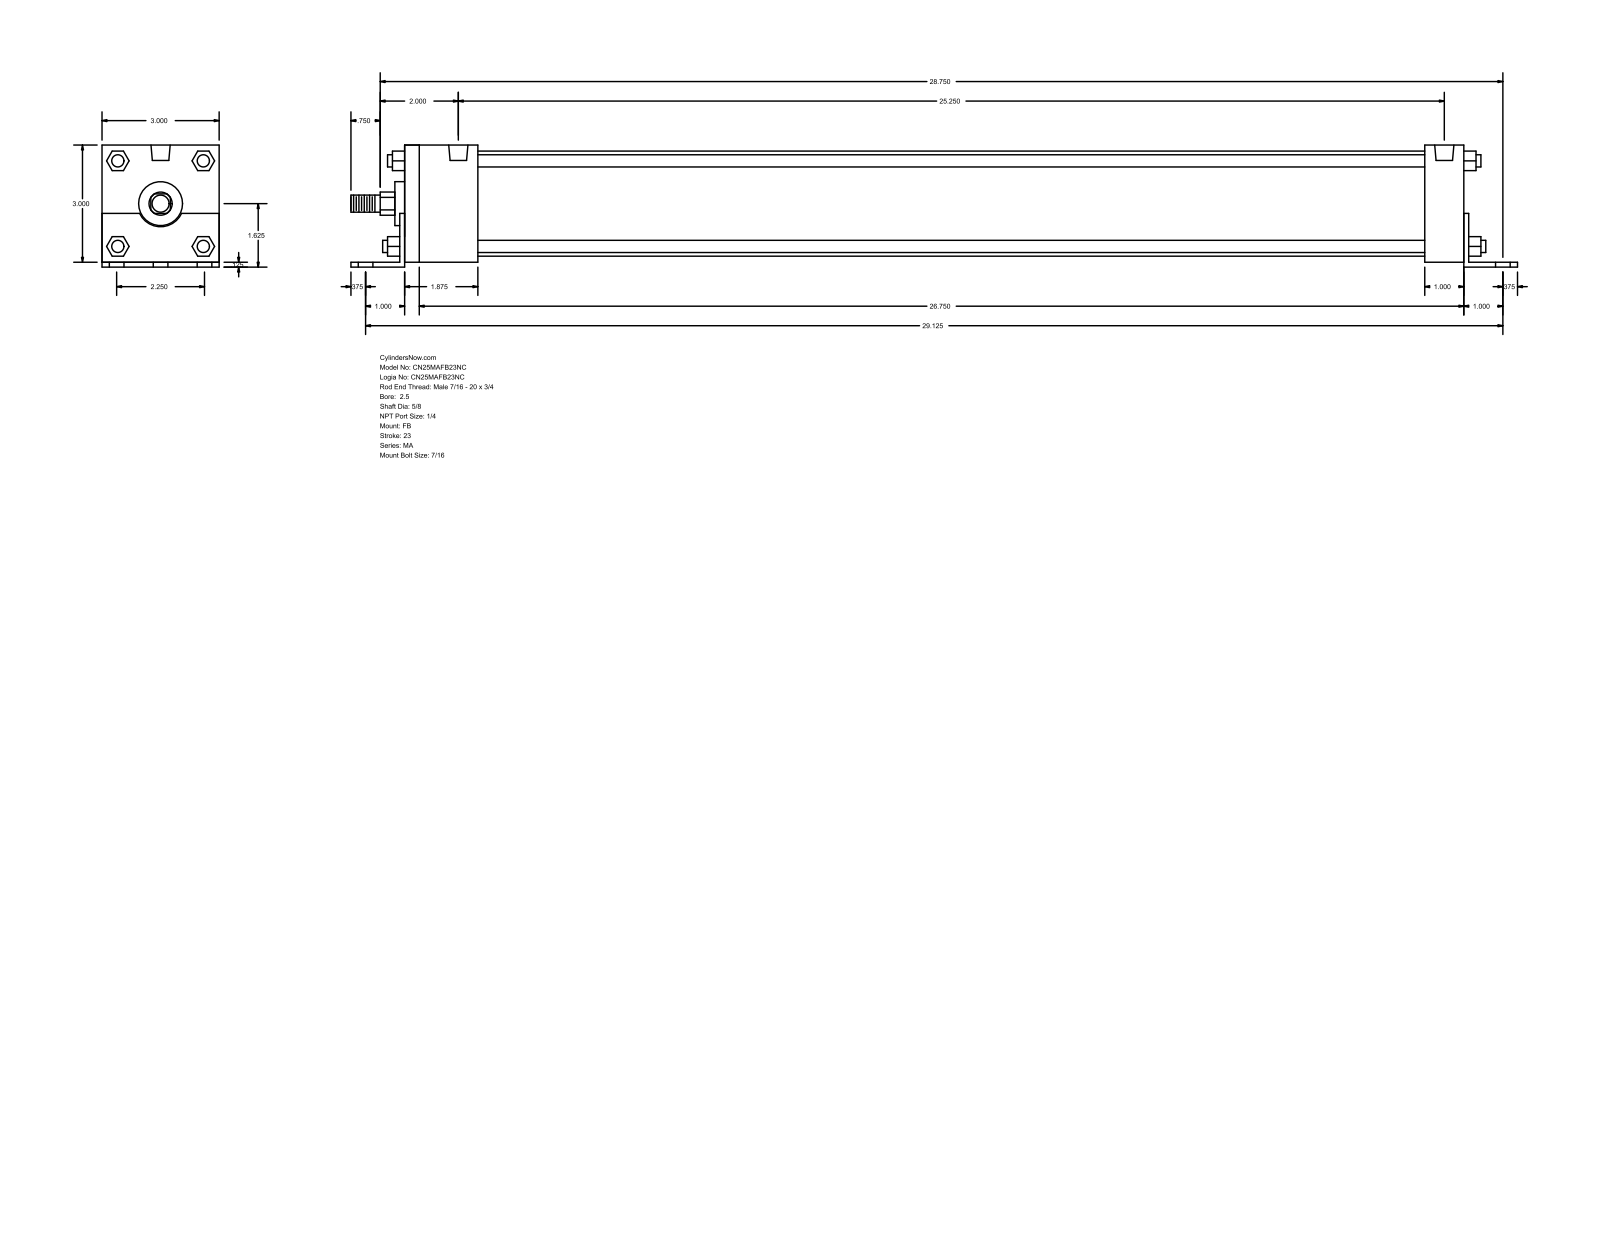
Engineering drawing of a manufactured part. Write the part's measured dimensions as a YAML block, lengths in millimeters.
part_name: "MA_FB__0250_0.625"
step_written_by: "GSSL Pune (CONFIG_CONTROL_DESIGN)"
units: millimeters
bodies: {solids: 0, faces: 140, planar: 105, cylindrical: 35, other: 0}
overall_size: [758.83, 79.38, 76.2]
round_holes:
  - {diameter: 11.11, count: 6}
  - {diameter: 7.94, count: 4}
  - {diameter: 12.49, count: 2}
round_bosses_or_shafts:
  - {diameter: 7.94, count: 4}
  - {diameter: 68.33, count: 1}
  - {diameter: 28.57, count: 1}
  - {diameter: 15.88, count: 1}
  - {diameter: 11.11, count: 1}
partial_cylinders:
  - {radius: 7.54, count: 1}
  - {radius: 15.05, count: 1}
face_to_face_distances: [76.2, 3.17, 79.37, 688.97, 695.32, 3.18, 692.14, 47.62, 25.4, 692.15]
hole_center_spacings: [28.57, 740.33, 739.78, 47.62, 57.14, 66.75, 641.35, 680.05]
